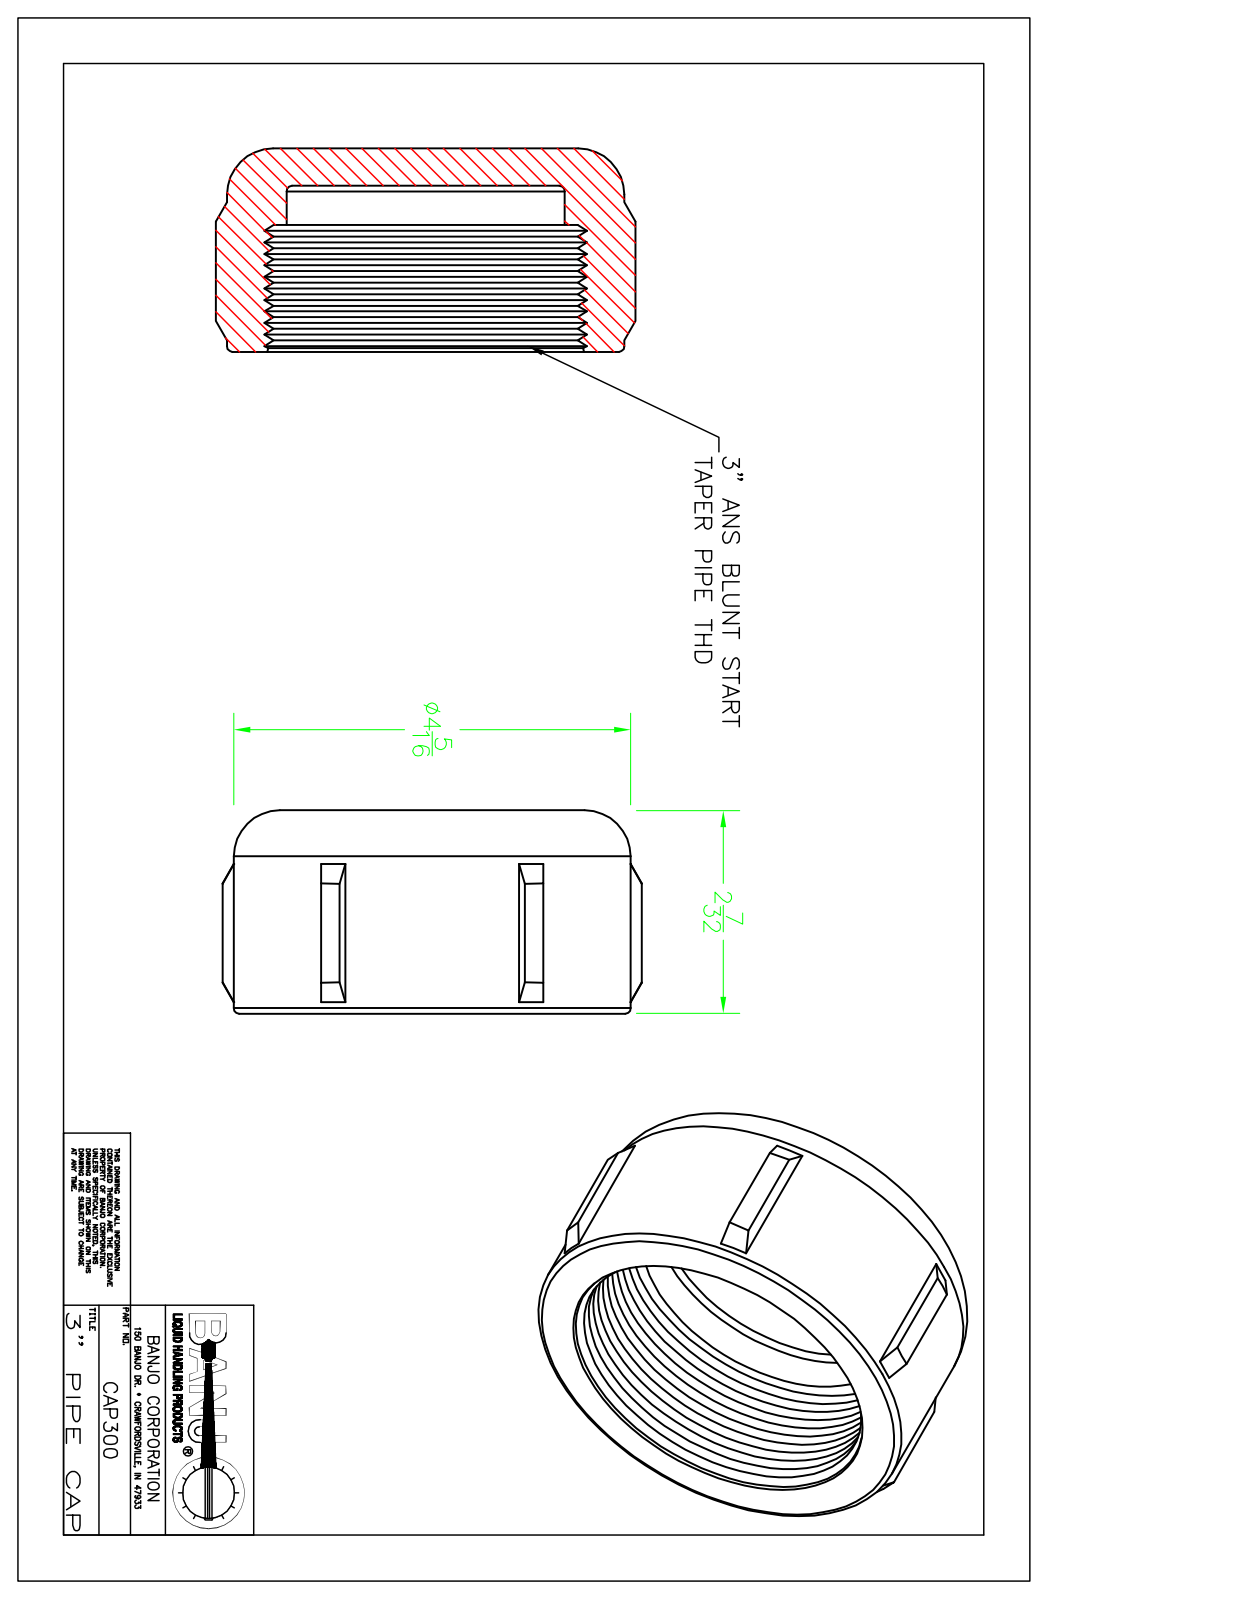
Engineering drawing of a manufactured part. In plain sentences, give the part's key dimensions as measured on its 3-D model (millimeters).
The part is named "CAP300". Its 3-D file was written by "Autodesk Inventor 2014 (AUTOMOTIVE_DESIGN)". It is 1 solid with 435 faces: 159 planar, 56 cylindrical and 220 other. Overall it measures 116.08 by 109.47 by 56.13 millimeters. Its volume is 271 510 cubic millimeters and its surface area 54 999 square millimeters. Round holes: 1 of diameter 76.71. Round bosses or shafts: 1 of diameter 109.47. Partial cylindrical surfaces (rounded edges, fillets, slot ends): 24 of radius 0.76, 1 of radius 24.66, 1 of radius 54.48. The main face-to-face distances are 10.41, 45.72, 56.13, 33.02, 12.7, 23.11, 116.08, 26.27, 89.81, 63.54.
